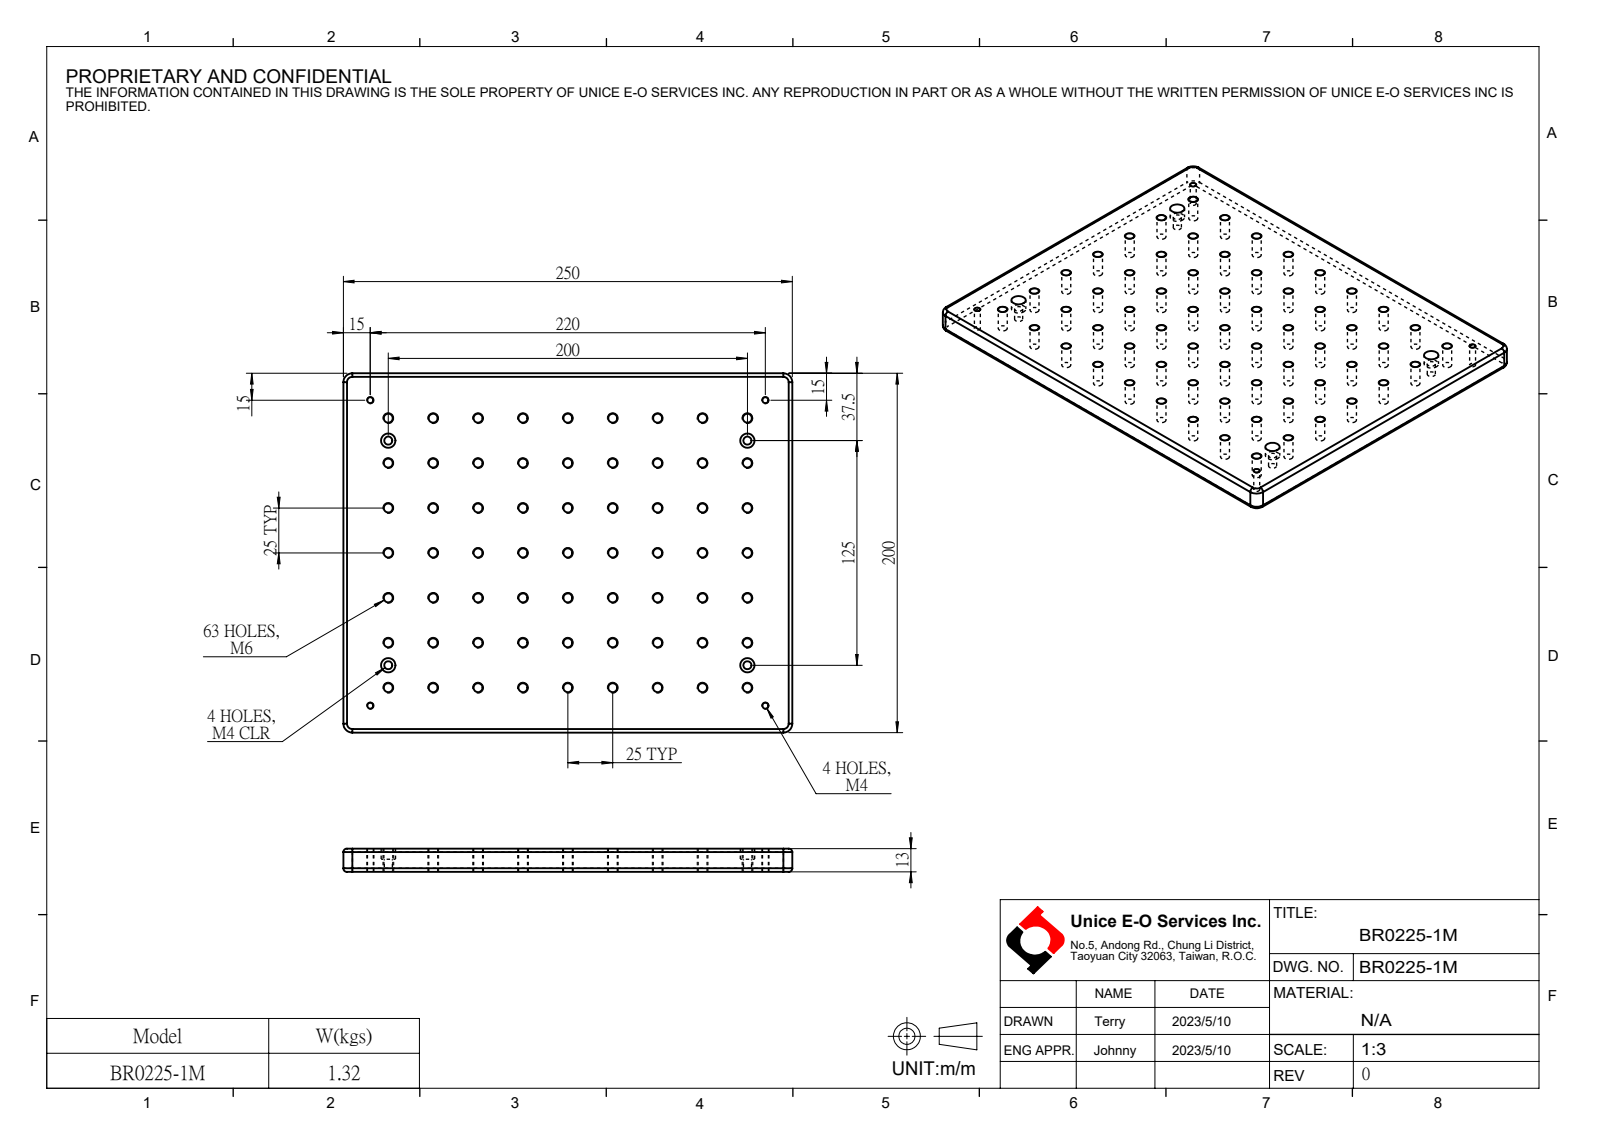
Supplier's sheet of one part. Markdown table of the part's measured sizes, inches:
| quantity | value |
| --- | --- |
| part name | BR0225-1M |
| STEP written by | SolidWorks 2022 (CONFIG_CONTROL_DESIGN) |
| units | inches |
| bodies | 1 solid, 180 faces (10 planar, 162 cylindrical, 8 other) |
| overall size | 9.843 × 7.874 × 0.512 |
| volume | 38.45 in³ |
| surface area | 188.7 in² |
| round holes (diameter × count) | 0.197 × 63, 0.13 × 4, 0.177 × 4, 0.315 × 4 |
| partial cylindrical surfaces (radius × count) | 0.079 × 8, 0.197 × 4 |
| main face-to-face distances | 0.512, 7.874, 9.843, 0.276, 0.236 |
| hole center spacings | 0.984, 1.969, 5.987, 2.953, 4.921, 6.225, 5.906, 6.603 |
